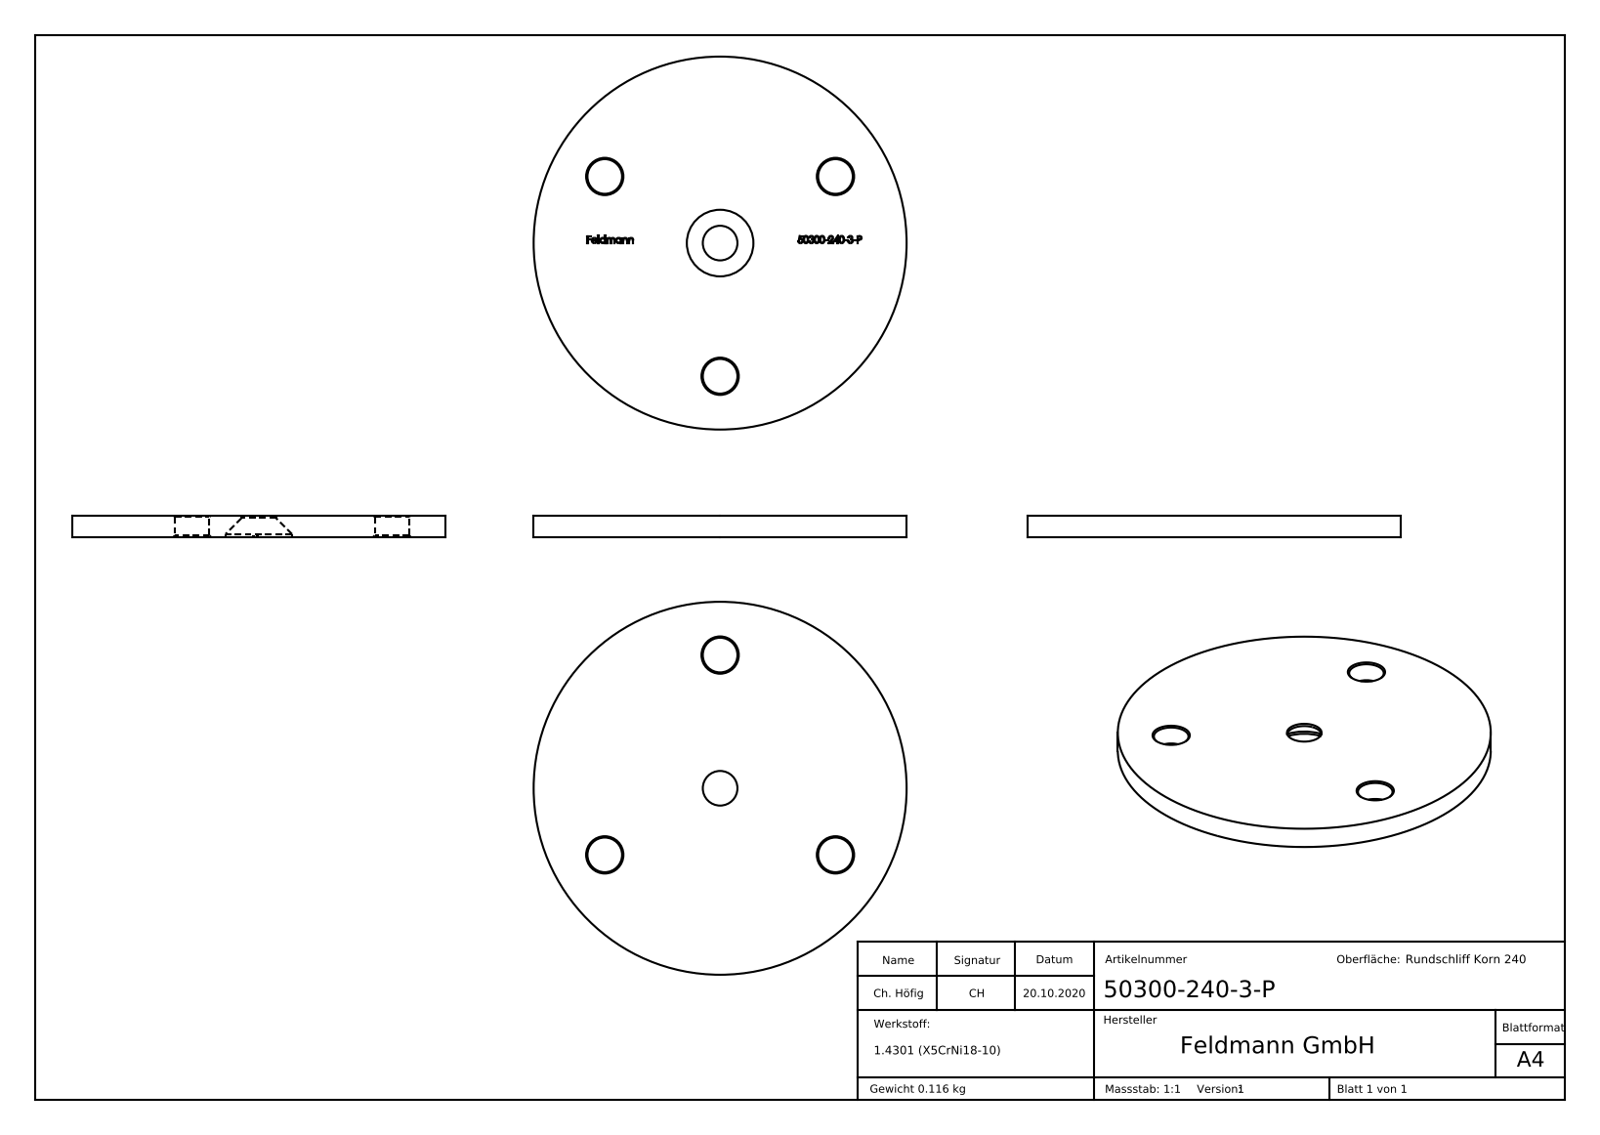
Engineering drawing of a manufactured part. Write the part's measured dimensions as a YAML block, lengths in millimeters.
part_name: "50300-240-3-P"
step_written_by: "SolidWorks 2018 (CONFIG_CONTROL_DESIGN)"
units: millimeters
bodies: {solids: 1, faces: 295, planar: 137, cylindrical: 12, other: 146}
overall_size: [70, 70, 4]
volume: 14693
surface_area: 8617
round_holes:
  - {diameter: 6.5, count: 4}
  - {diameter: 12.5, count: 1}
round_bosses_or_shafts:
  - {diameter: 70, count: 1}
face_to_face_distances: [4, 3.9, 0.44, 0.39, 0.58, 2.97, 0.88, 2.02, 50.66, 48.64]
hole_center_spacings: [25, 43.3]
